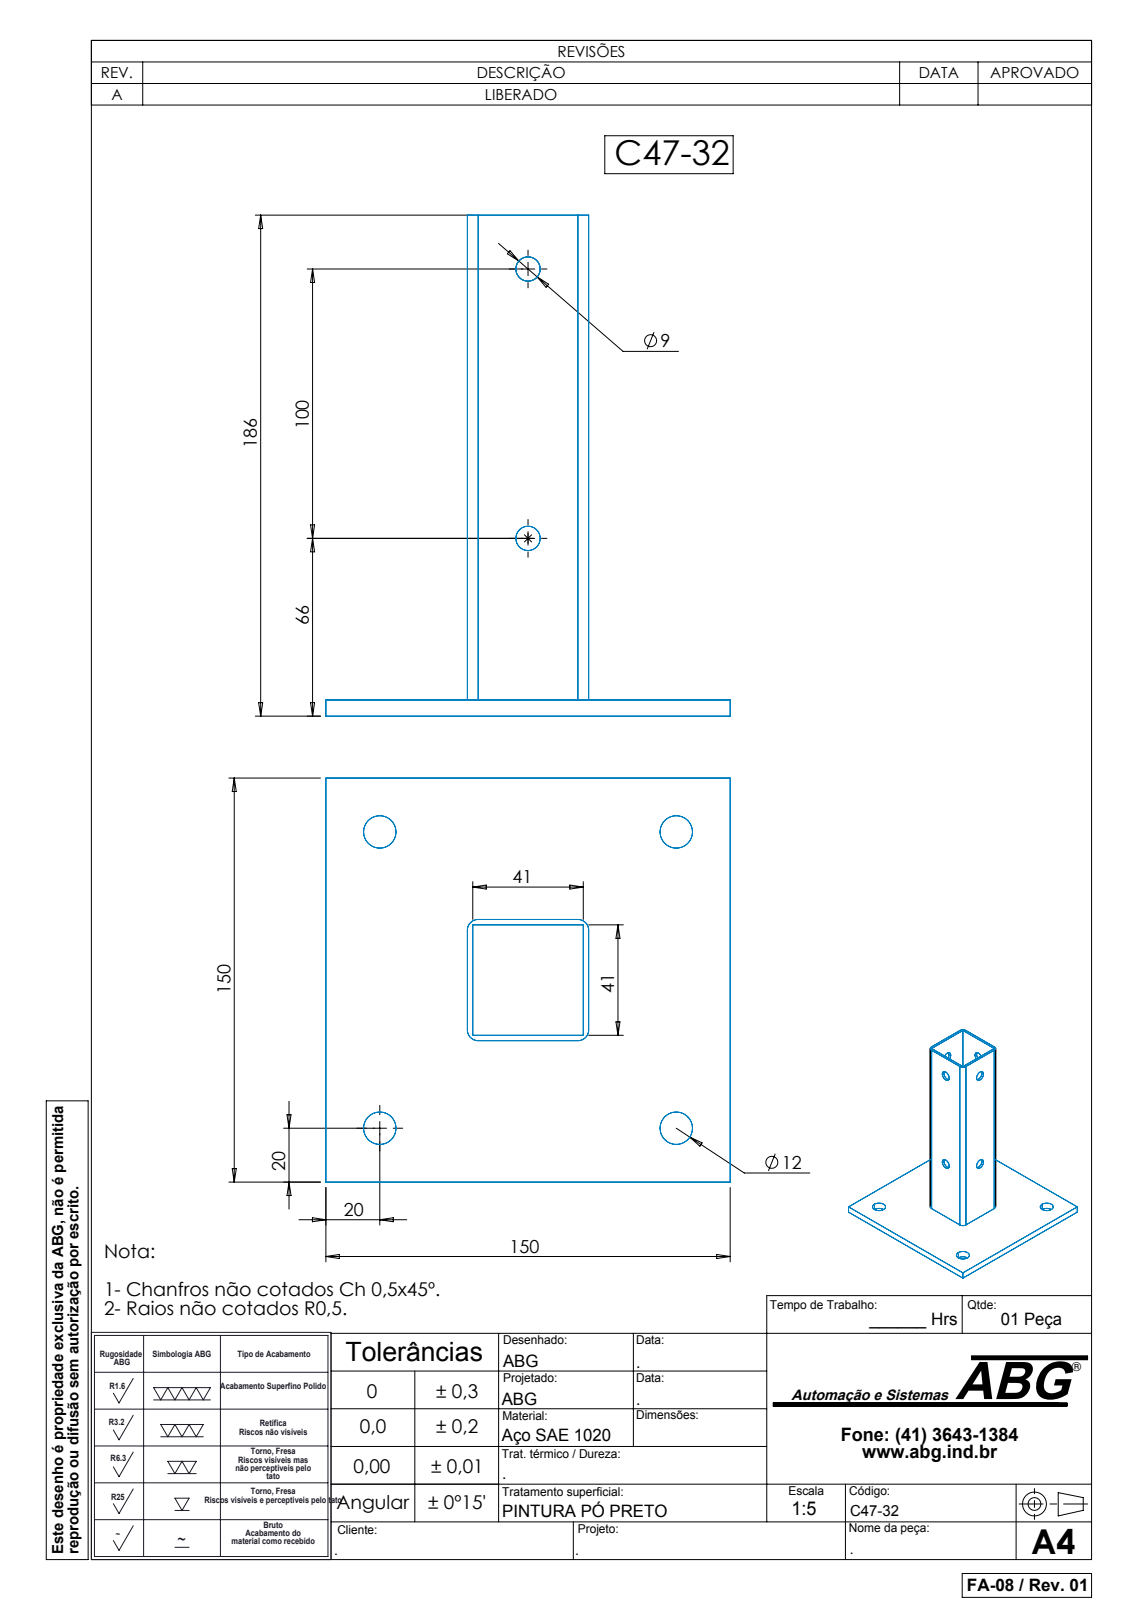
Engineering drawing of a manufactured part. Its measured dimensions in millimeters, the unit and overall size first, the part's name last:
Units: millimetres
Overall size (bounding box): 186 × 150 × 150
Round holes (diameter × count): ⌀9 ×4, ⌀12 ×4
Partial cylindrical surfaces — rounded edges, fillets, slot ends (radius × count): R4 ×4
Main face-to-face distances: 2, 43, 6, 41, 45, 52.5, 54.5, 95.5, 97.5, 150
Hole centre spacings: 110, 100, 155.56
Volume: 190 716 mm³ · Surface area: 108 718 mm²
Bodies: 1 solid, 44 faces (16 planar, 28 cylindrical, 0 other)
Part name (STEP PRODUCT): C47-32
STEP written by: SolidWorks 2007 (CONFIG_CONTROL_DESIGN)
